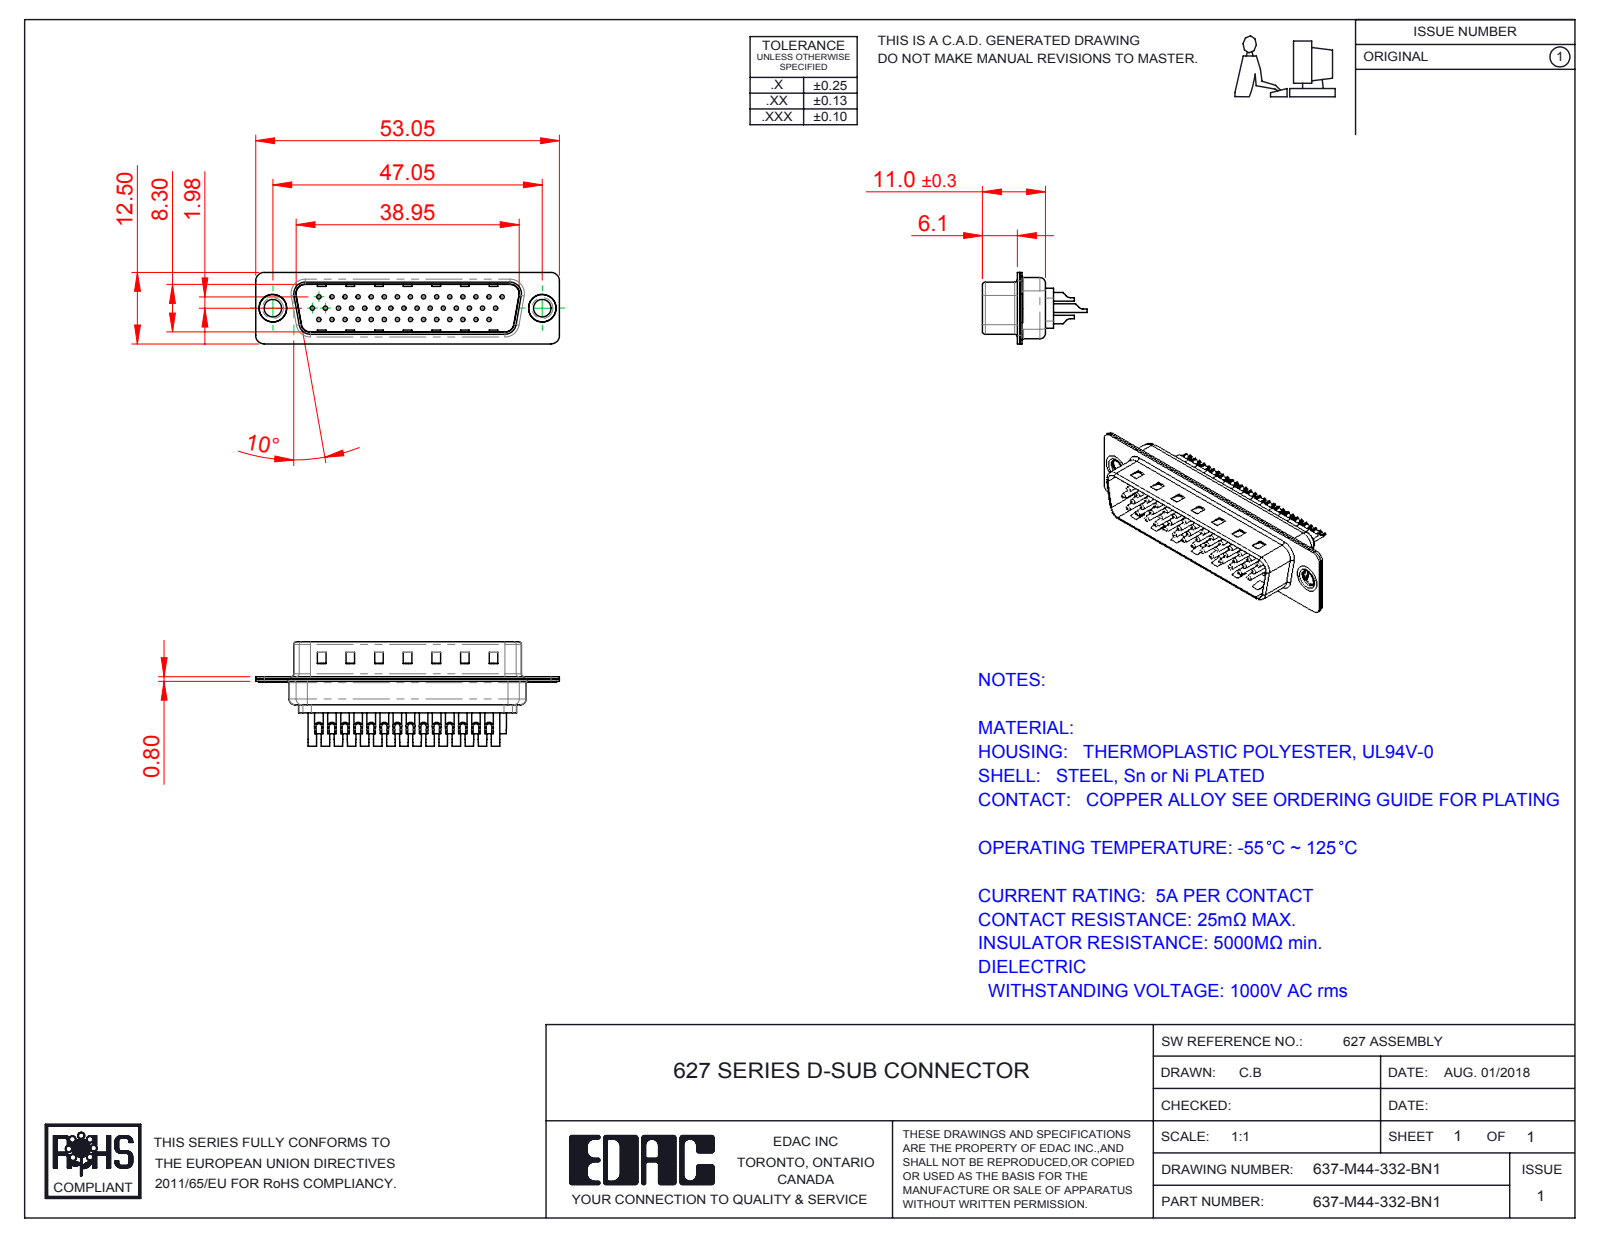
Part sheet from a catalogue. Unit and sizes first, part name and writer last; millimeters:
Units: millimetres
Overall size (bounding box): 53.05 × 18.25 × 12.5
Round holes (diameter × count): ⌀0.75 ×44, ⌀1 ×44, ⌀1.6 ×44, ⌀2 ×44, ⌀3.05 ×2, ⌀4 ×2, ⌀4.8 ×2
Round bosses / shafts (diameter × count): ⌀1.5 ×44, ⌀2 ×3, ⌀0.75 ×3, ⌀5 ×2, ⌀4.9 ×2, ⌀3.55 ×2
Partial cylindrical surfaces — rounded edges, fillets, slot ends (radius × count): R1.5 ×16, R2 ×12, R0.5 ×8, R1.6 ×8, R1 ×7, R0.25 ×4, R0.6 ×4, R0.65 ×4
Main face-to-face distances: 0.4, 0.8, 9.5, 9.1, 8.7, 9.9, 0.75, 1.1, 0.35, 1.2
Hole centre spacings: 2.28, 3.96, 2.29, 4.57, 8.24, 6.86, 11.43, 14.99
Volume: 2 896 mm³ · Surface area: 8 864 mm²
Bodies: 49 solids, 1978 faces (567 planar, 825 cylindrical, 586 other)
Part name (STEP PRODUCT): 637M Thru Hole Rivet; 637-M44-332-BN1; 637M Housing_44 Contacts; 637M Shell Front_44 Contacts (+4 more)
STEP written by: SolidWorks 2016 (CONFIG_CONTROL_DESIGN)
